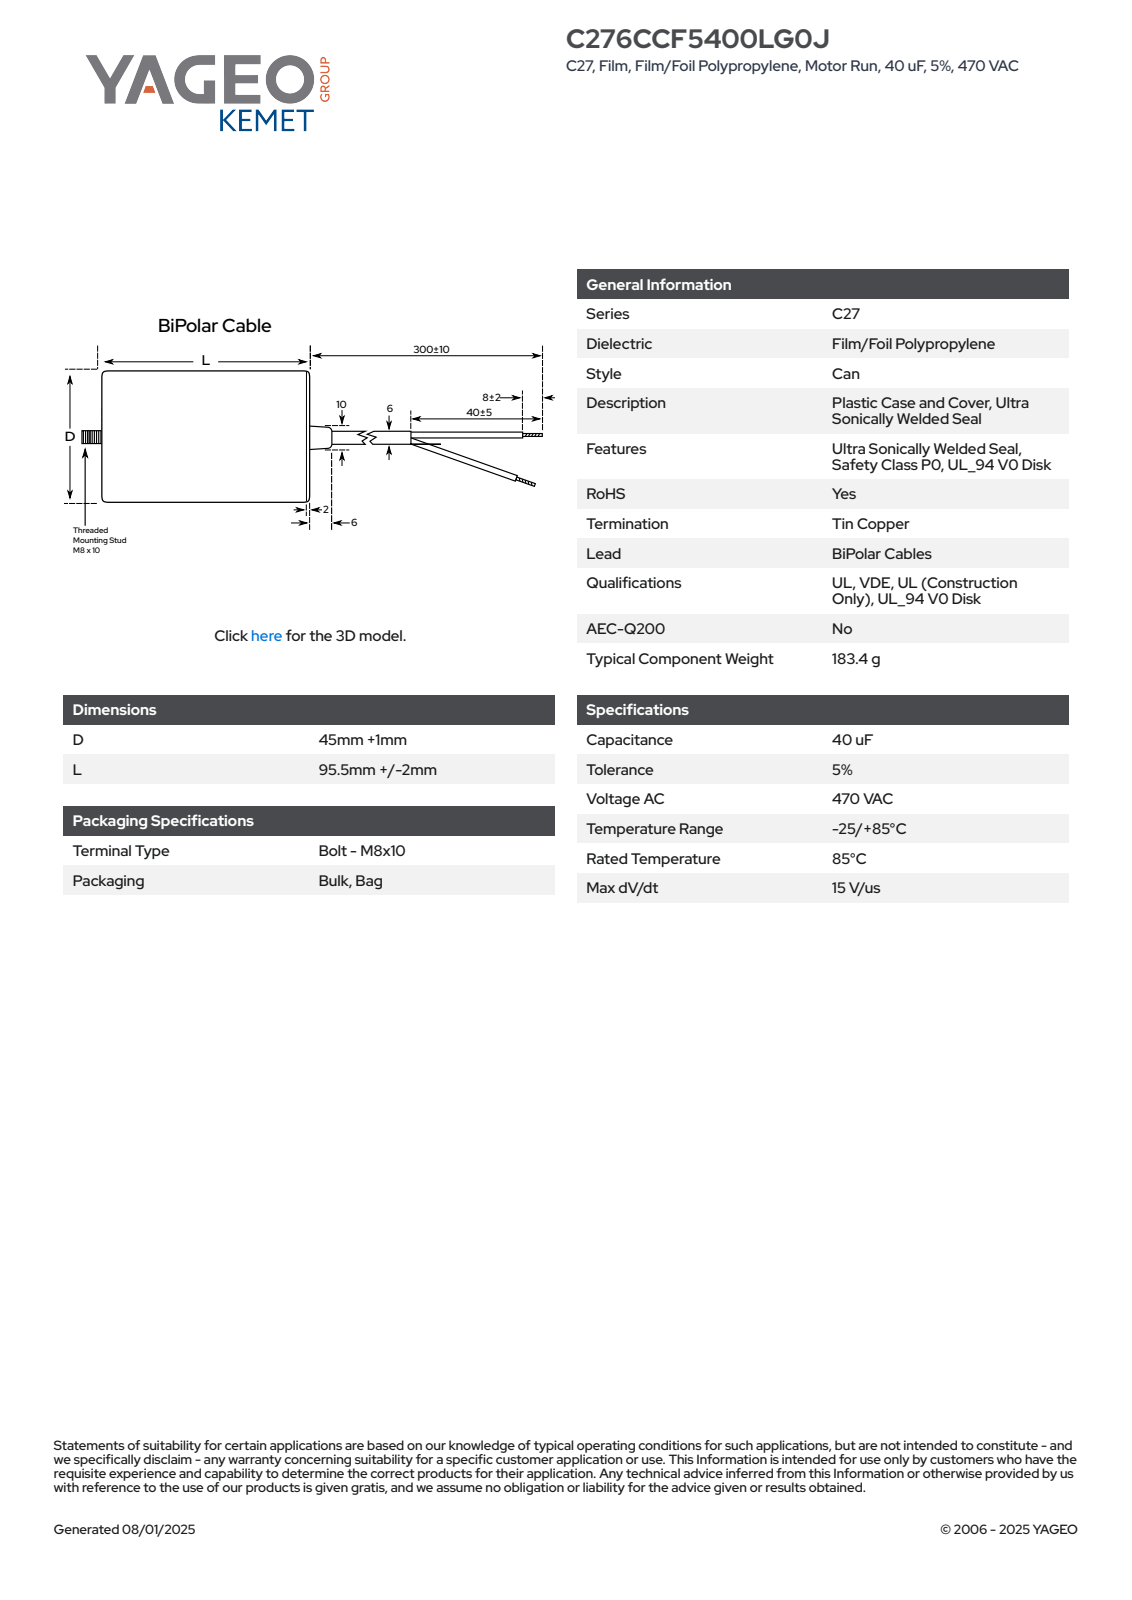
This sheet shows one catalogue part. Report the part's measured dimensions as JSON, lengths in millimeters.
{"part_name": "CFM_KC27BI_45X95.5_D46L97.5", "step_written_by": "SolidWorks 2014 (AUTOMOTIVE_DESIGN)", "units": "millimeters", "bodies": {"solids": 2, "faces": 82, "planar": 28, "cylindrical": 15, "other": 39}, "overall_size": [113.5, 46.01, 46], "volume_mm3": 160087, "surface_area_mm2": 18099, "round_holes": [[42, 1]], "round_bosses_or_shafts": [[46, 1], [8, 1]], "partial_cylinders_radius": [[23.01, 1]], "face_to_face_distances": [95.5, 97.5, 2, 10, 105.5, 107.5, 113.5, 103.5, 8, 6]}
